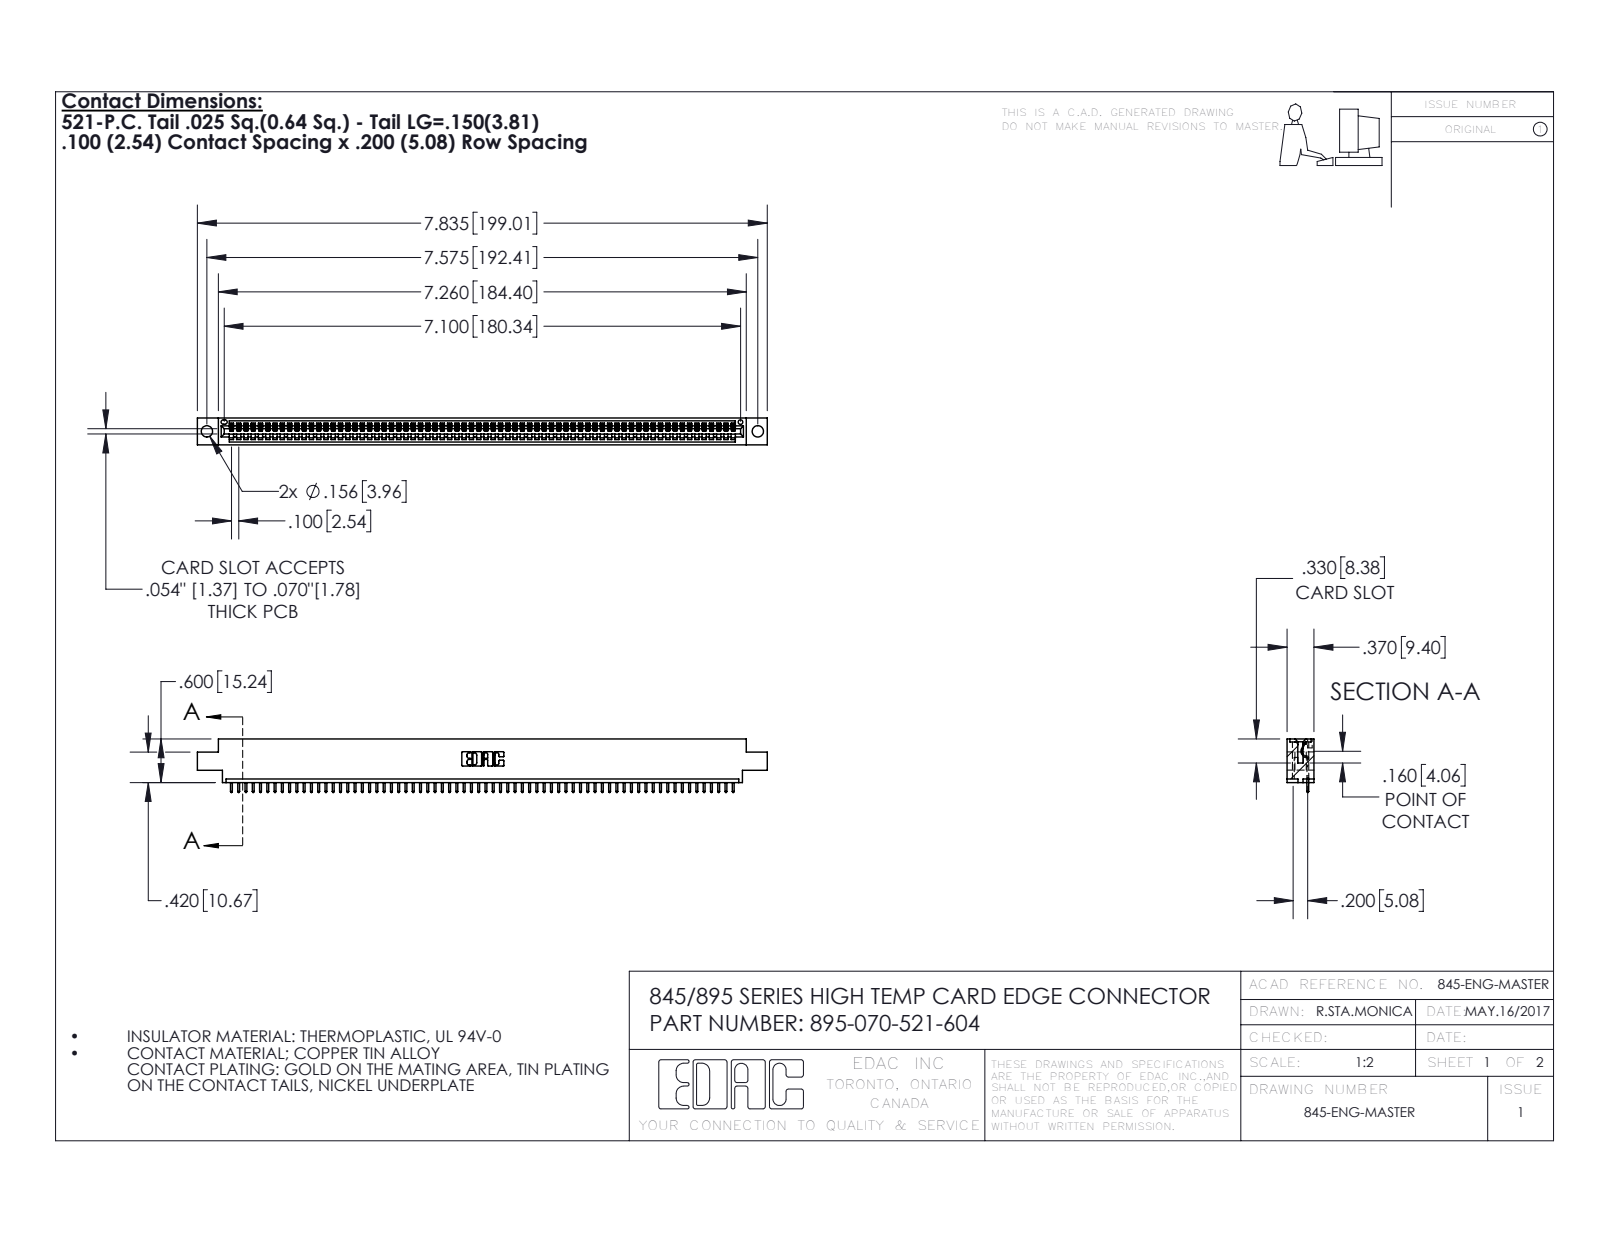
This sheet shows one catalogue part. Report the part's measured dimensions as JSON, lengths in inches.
{"part_name": "345-292-001_345-293-121; 345 Part_0.170 Offset - 0.156 Dia-TH; 395-070-521-604", "step_written_by": "SolidWorks 2016 (CONFIG_CONTROL_DESIGN)", "units": "inches", "bodies": {"solids": 71, "faces": 4190, "planar": 2884, "cylindrical": 1306, "other": 0}, "overall_size": [7.835, 0.737, 0.37], "volume_in3": 1.143, "surface_area_in2": 37.86, "round_holes": [[0.156, 2], [0.064, 1]], "partial_cylinders_radius": [[0.006, 140], [0.01, 140], [0.01, 22], [0.007, 6], [0.031, 6], [0.026, 3], [0.031, 2], [0.04, 2]], "face_to_face_distances": [0.298, 0.072, 0.37, 0.2, 0.098, 0.272, 0.025, 0.225, 0.175, 0.149], "hole_center_spacings": [0.27, 7.339, 7.575]}
